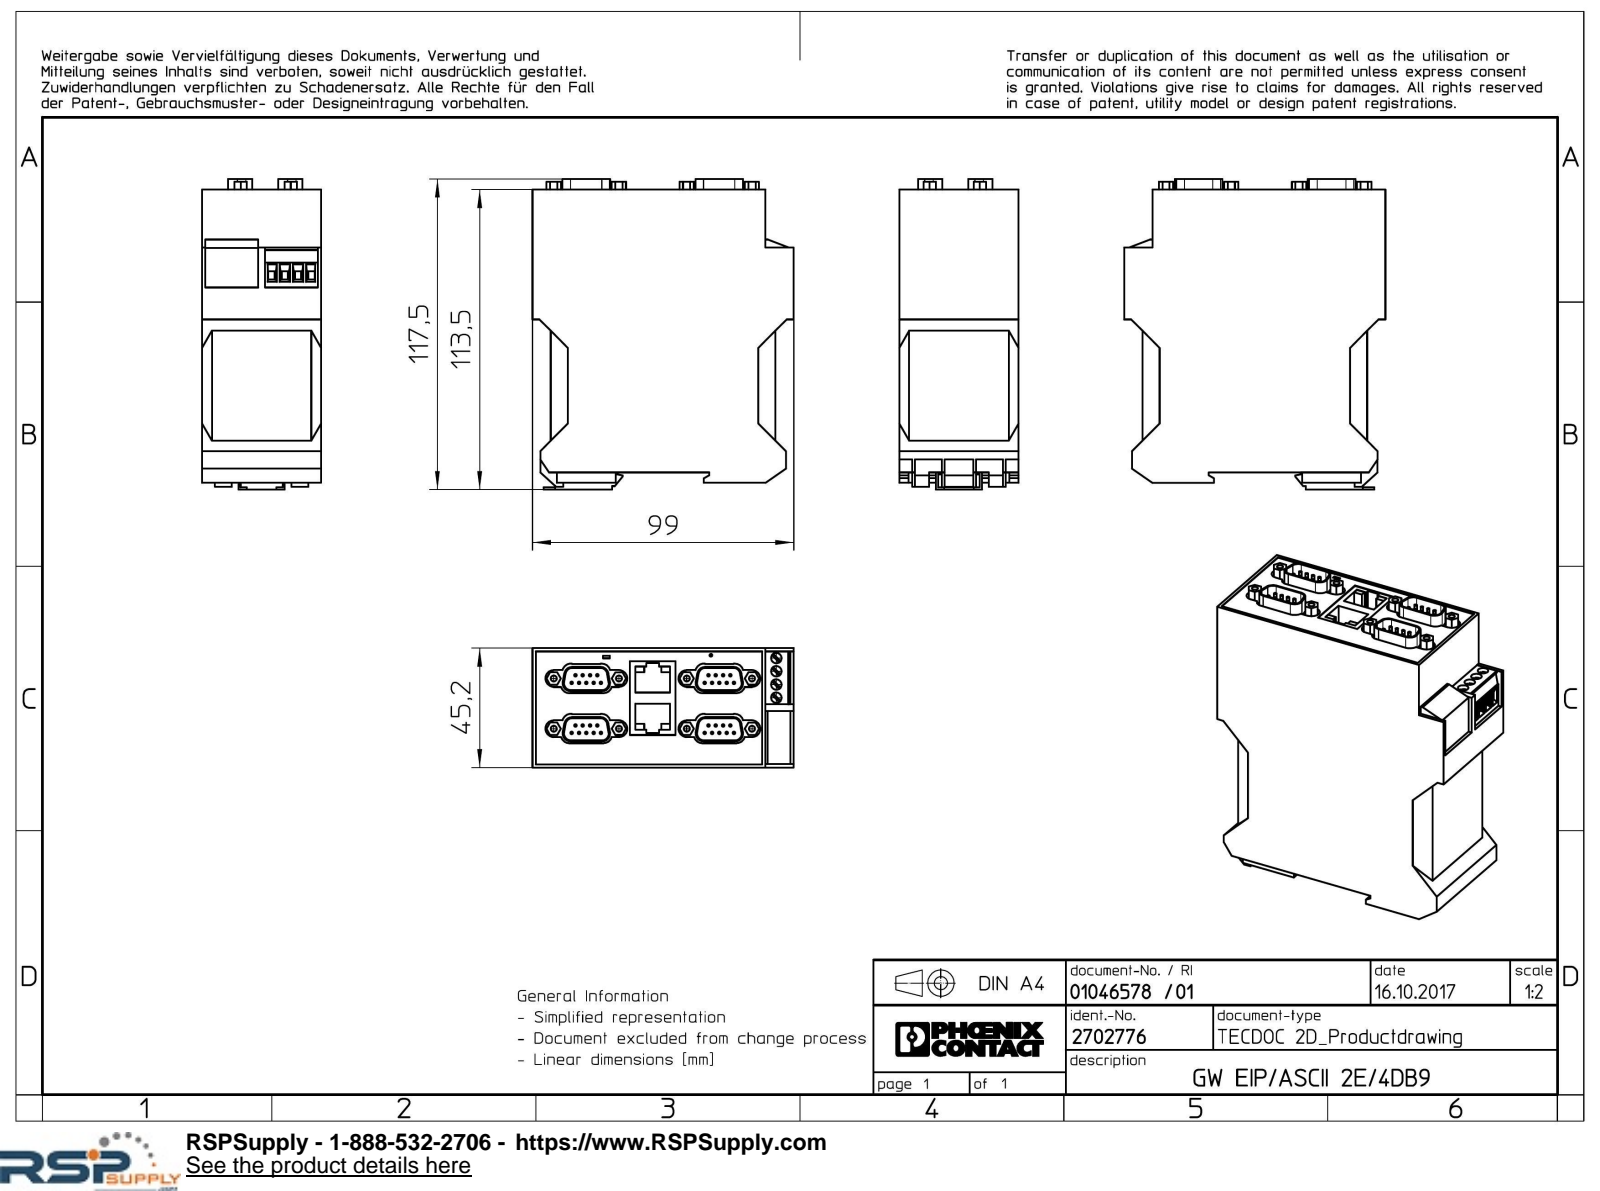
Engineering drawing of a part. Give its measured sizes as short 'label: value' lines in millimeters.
name: GW...ASCII_2E_4DB9-select
written by: Creo Elements/Direct Modeling 18.1I 14-Aug-2016 (C) Parametric Technology GmbH (AUTOMOTIVE_DESIGN)
unit: mm
bodies: 1 solid, 568 faces (414 planar, 154 cylindrical, 0 other)
size: 117.5 × 99 × 45.2
volume: 437 141 mm³; area: 45 719 mm²
holes: 8× ⌀2.29, 4× ⌀4, 1× ⌀1.08
bosses: 36× ⌀1
rounds: 24× R3.17, 16× R2.54, 16× R3.04
face distances: 45.2, 4, 92.05, 6.95, 106.8, 85.1, 110.8, 3.75, 2, 88.3
hole spacings: 19, 24.74, 31.19, 50.4, 53.86, 5, 10, 25.66
